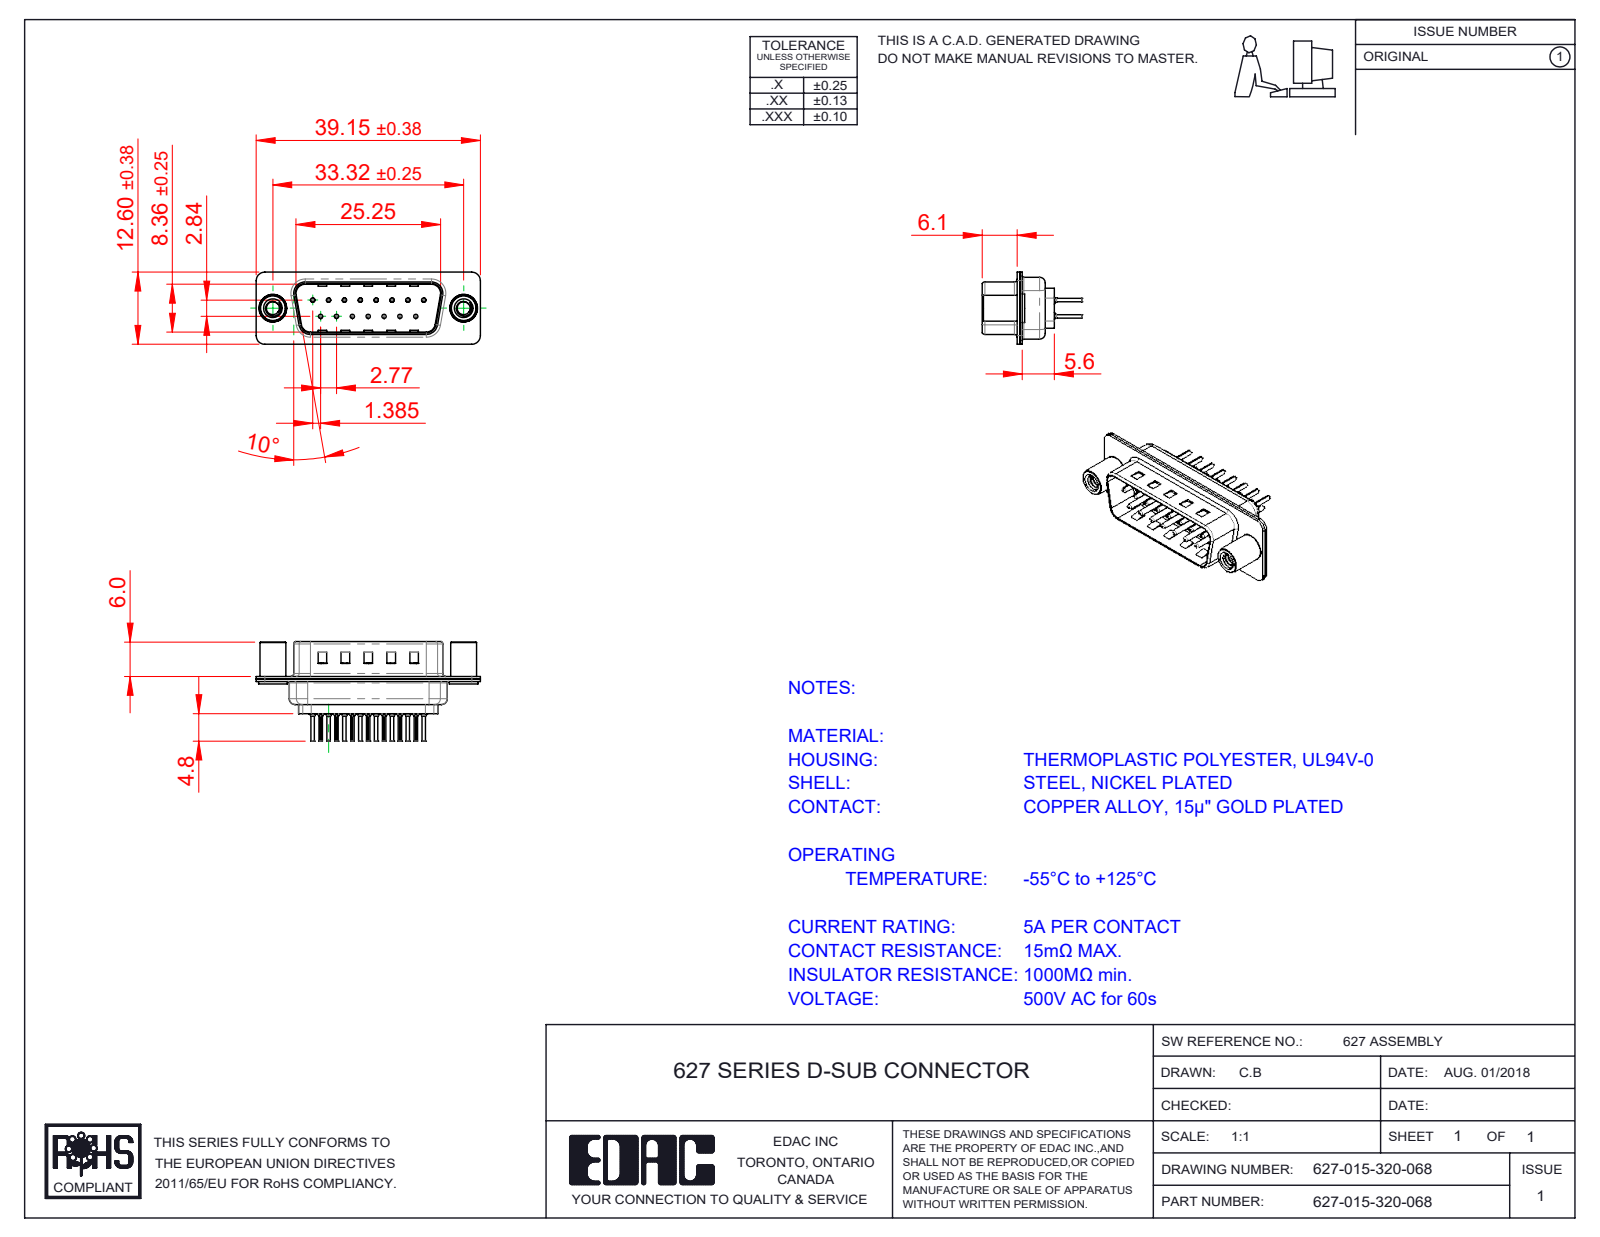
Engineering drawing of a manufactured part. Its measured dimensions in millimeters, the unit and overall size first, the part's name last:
Units: millimetres
Overall size (bounding box): 39.15 × 17.3 × 12.6
Round holes (diameter × count): ⌀0.2 ×15, ⌀0.35 ×15, ⌀1.1 ×15, ⌀1.6 ×15, ⌀2.26 ×2, ⌀4 ×2, ⌀4.8 ×2
Round bosses / shafts (diameter × count): ⌀2 ×15, ⌀1.5 ×15, ⌀0.75 ×15, ⌀0.6 ×15, ⌀5 ×2, ⌀4.9 ×2, ⌀4.5 ×2
Partial cylindrical surfaces — rounded edges, fillets, slot ends (radius × count): R0.1 ×30, R1.5 ×16, R2 ×12, R0.5 ×8, R1.6 ×8, R0.25 ×4, R0.6 ×4, R0.65 ×4
Main face-to-face distances: 0.4, 0.45, 0.9, 0.82, 9.58, 8.76, 1.5, 1.4, 6.5, 5.6
Hole centre spacings: 3.16, 2.77, 5.54, 8.31, 11.08, 5.03, 5.04, 7.48
Volume: 1 894 mm³ · Surface area: 5 587 mm²
Bodies: 20 solids, 1844 faces (501 planar, 716 cylindrical, 627 other)
Part name (STEP PRODUCT): 627 Shell Front_15 Contacts; 627 4-40 Threaded Standoff; 627 Contact Row 1_20L; 627-015-320-068 (+3 more)
STEP written by: SolidWorks 2020 (CONFIG_CONTROL_DESIGN)
